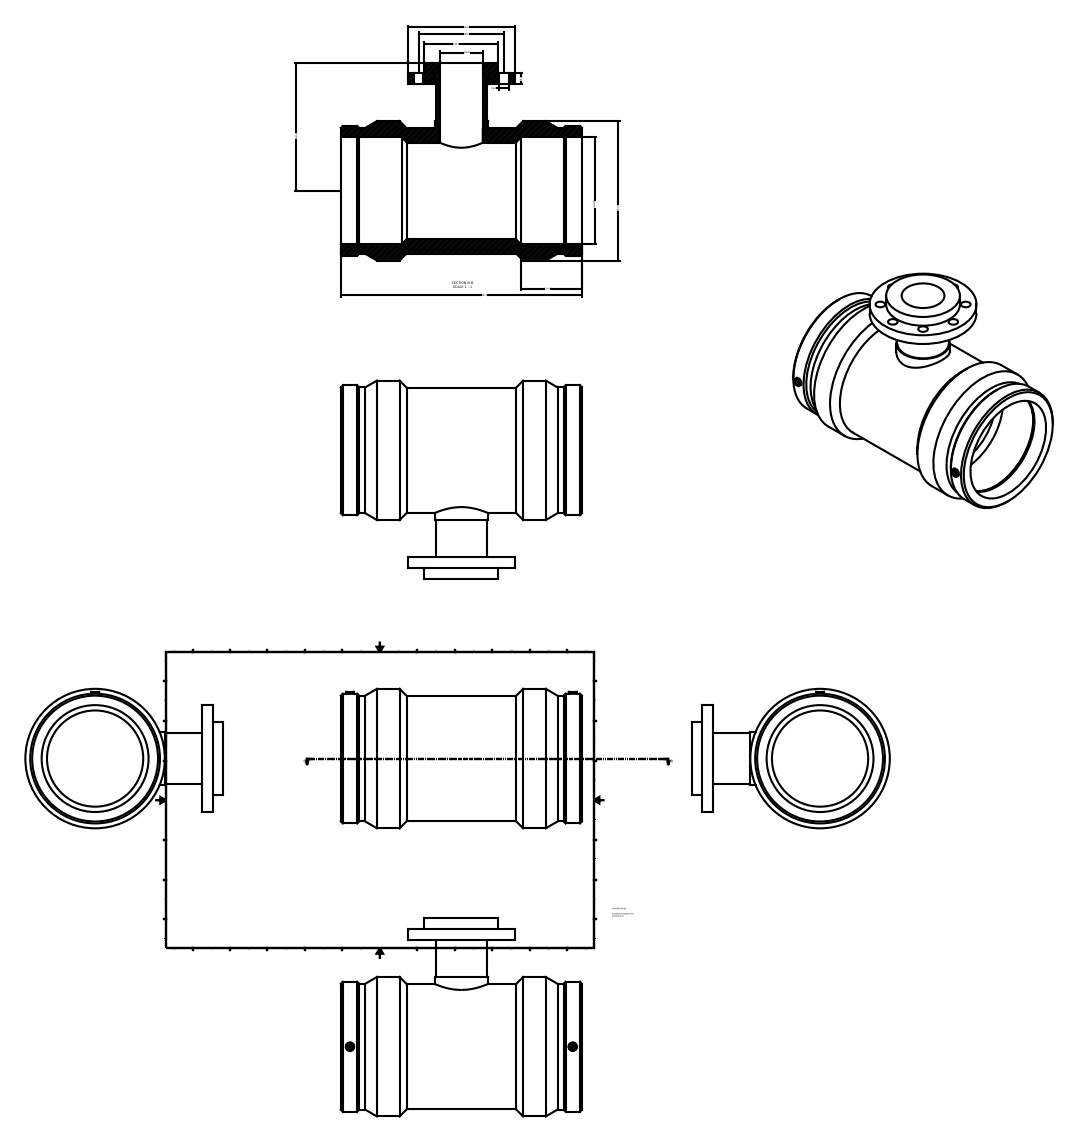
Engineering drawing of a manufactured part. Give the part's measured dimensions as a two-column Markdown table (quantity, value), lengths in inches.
| quantity | value |
| --- | --- |
| part name | 499404200080 |
| STEP written by | Autodesk Inventor 2015 (AUTOMOTIVE_DESIGN) |
| units | inches |
| bodies | 1 solid, 60 faces (14 planar, 30 cylindrical, 16 other) |
| overall size | 17.756 × 14.587 × 10.276 |
| volume | 535.6 in³ |
| surface area | 1 249 in² |
| round holes (diameter × count) | 0.709 × 8, 0.394 × 2, 3.15 × 1, 4.094 × 1, 7.087 × 1, 7.874 × 1 |
| round bosses / shafts (diameter × count) | 0.157 × 2, 10.276 × 1, 9.556 × 1, 9.27 × 1, 9.248 × 1, 7.874 × 1, 5.433 × 1, 3.937 × 1 |
| main face-to-face distances | 0.787, 17.756, 1.575, 1.342, 16.414, 4.311, 3.524, 2.736, 15.072, 0.551 |
| hole center spacings | 2.411, 3.15, 4.454, 5.82, 6.299, 16.409 |
